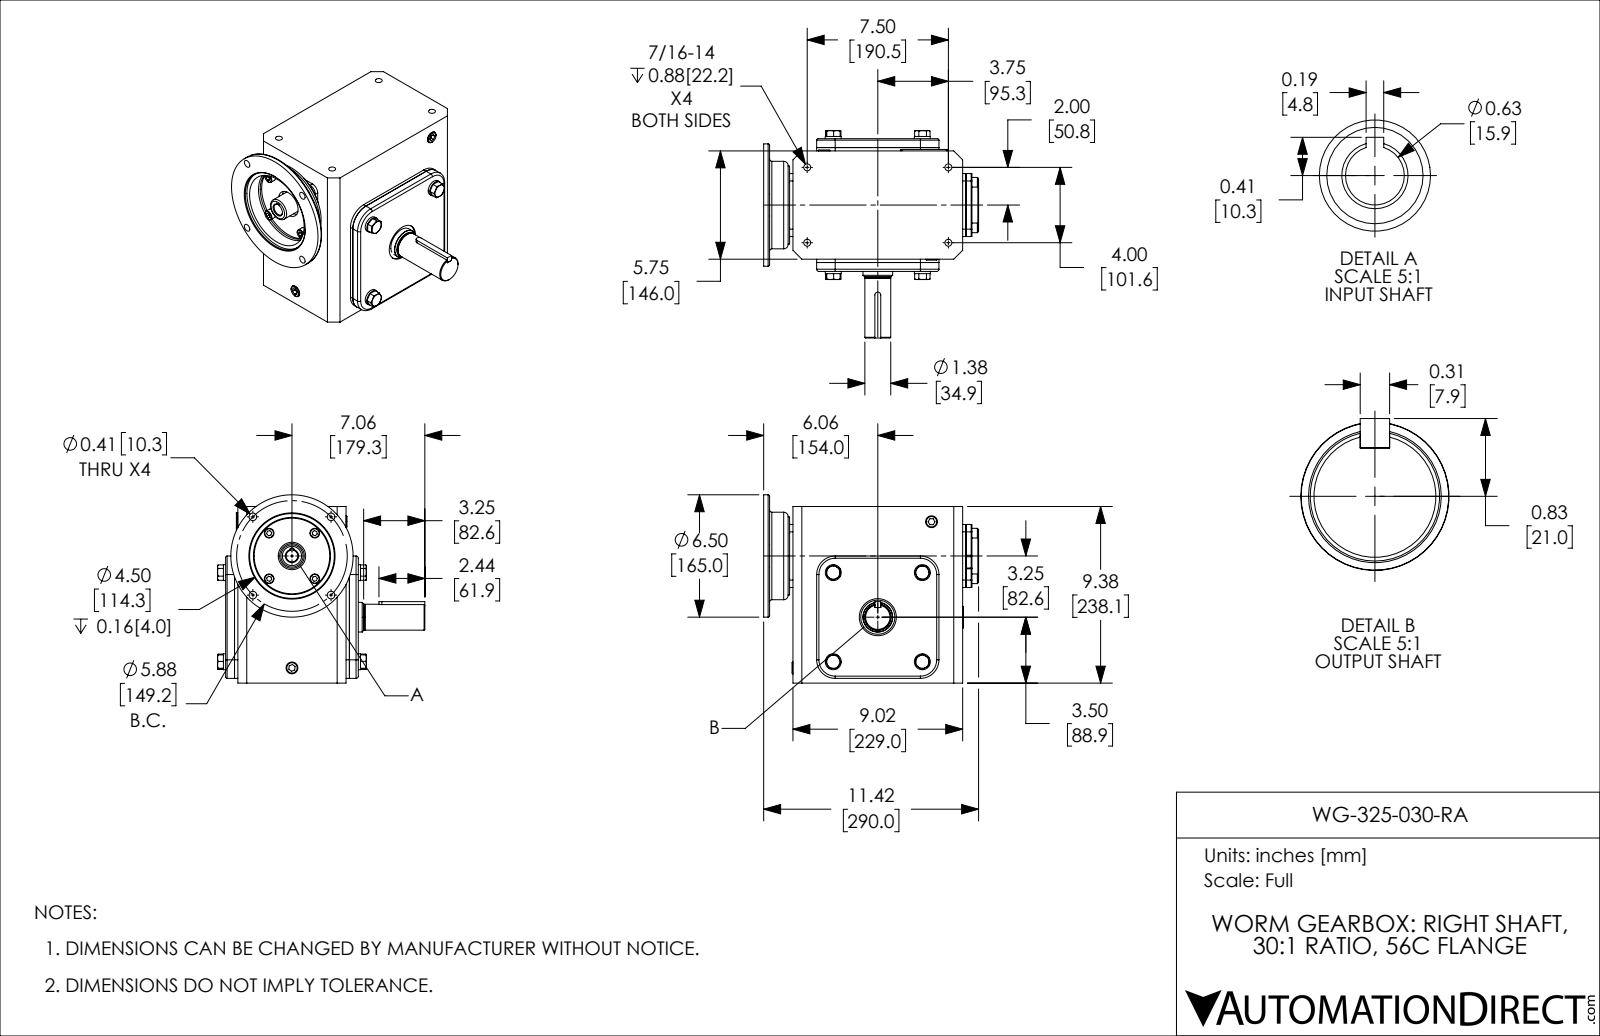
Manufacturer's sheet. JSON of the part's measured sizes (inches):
{"part_name": "WG-325-030-RA", "step_written_by": "SolidWorks 2017 (AUTOMOTIVE_DESIGN)", "units": "inches", "bodies": {"solids": 39, "faces": 576, "planar": 318, "cylindrical": 168, "other": 90}, "overall_size": [11.417, 11.014, 9.998], "volume_in3": 503.5, "surface_area_in2": 897.2, "round_holes": [[0.368, 4], [0.406, 4], [0.628, 3], [0.591, 1], [0.625, 1], [0.978, 1], [1.181, 1], [1.457, 1], [1.969, 1], [2.441, 1], [2.756, 1], [4.016, 1]], "round_bosses_or_shafts": [[0.846, 4], [0.512, 4], [6.496, 1], [4.646, 1], [4.134, 1], [2.835, 1], [1.575, 1], [1.375, 1]], "partial_cylinders_radius": [[0.079, 11], [0.118, 4], [0.394, 4], [0.906, 4], [0.984, 4], [0.02, 2], [0.039, 2], [0.156, 1]], "face_to_face_distances": [0.079, 0.177, 6.496, 0.394, 6.969, 0.472, 6.575, 6.398, 0.571, 0.65], "hole_center_spacings": [2.937, 4.154, 2.385, 4, 4.389, 5.718, 5.817, 5.875]}
